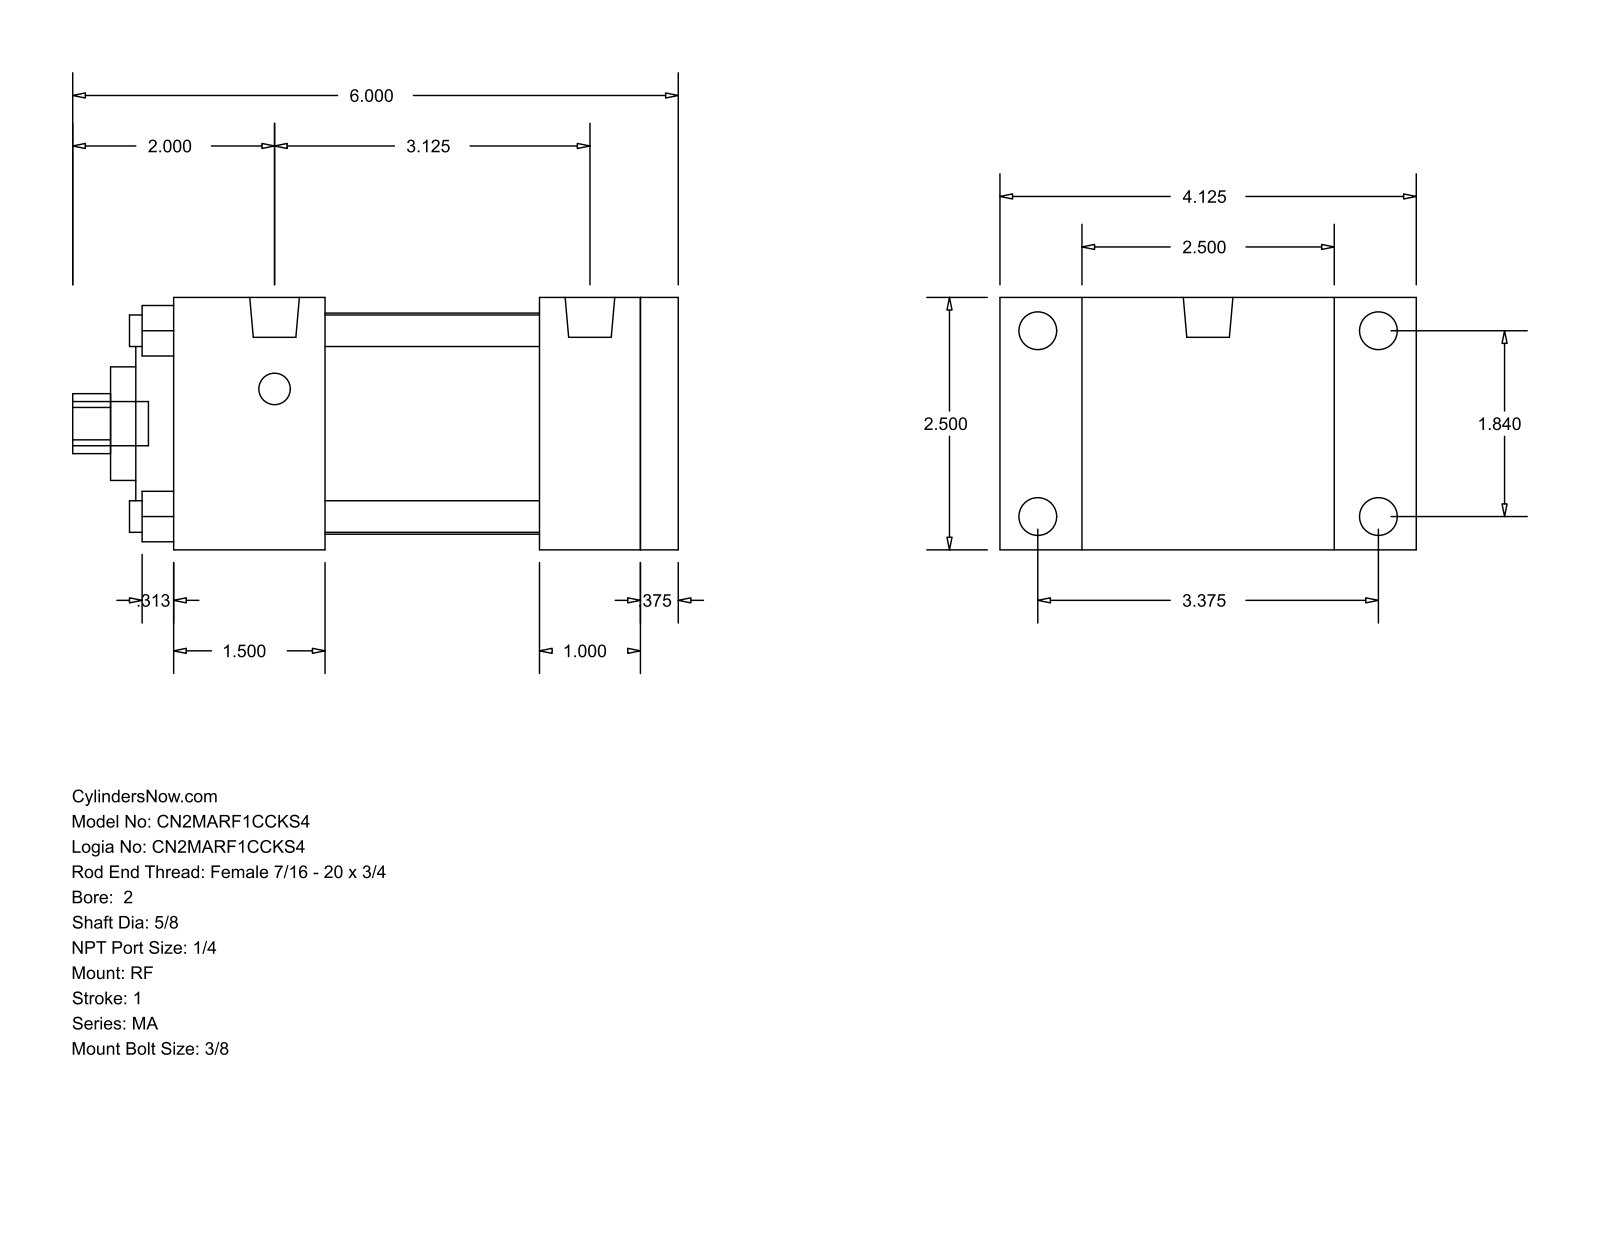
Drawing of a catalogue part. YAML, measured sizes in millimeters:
part_name: "MA_RF__0200_0.625"
step_written_by: "GSSL Pune (CONFIG_CONTROL_DESIGN)"
units: millimeters
bodies: {solids: 0, faces: 94, planar: 65, cylindrical: 29, other: 0}
overall_size: [152.4, 104.78, 63.5]
round_holes:
  - {diameter: 7.94, count: 4}
  - {diameter: 15.88, count: 1}
  - {diameter: 28.57, count: 1}
  - {diameter: 50.8, count: 1}
  - {diameter: 55.63, count: 1}
round_bosses_or_shafts:
  - {diameter: 9.53, count: 4}
  - {diameter: 7.94, count: 4}
  - {diameter: 12.49, count: 2}
  - {diameter: 11.11, count: 1}
partial_cylinders:
  - {radius: 7.54, count: 1}
face_to_face_distances: [63.5, 9.52, 127, 53.97, 38.1, 117.48, 79.38, 88.9, 92.07, 25.41]
hole_center_spacings: [33.05, 46.74, 66.1]
